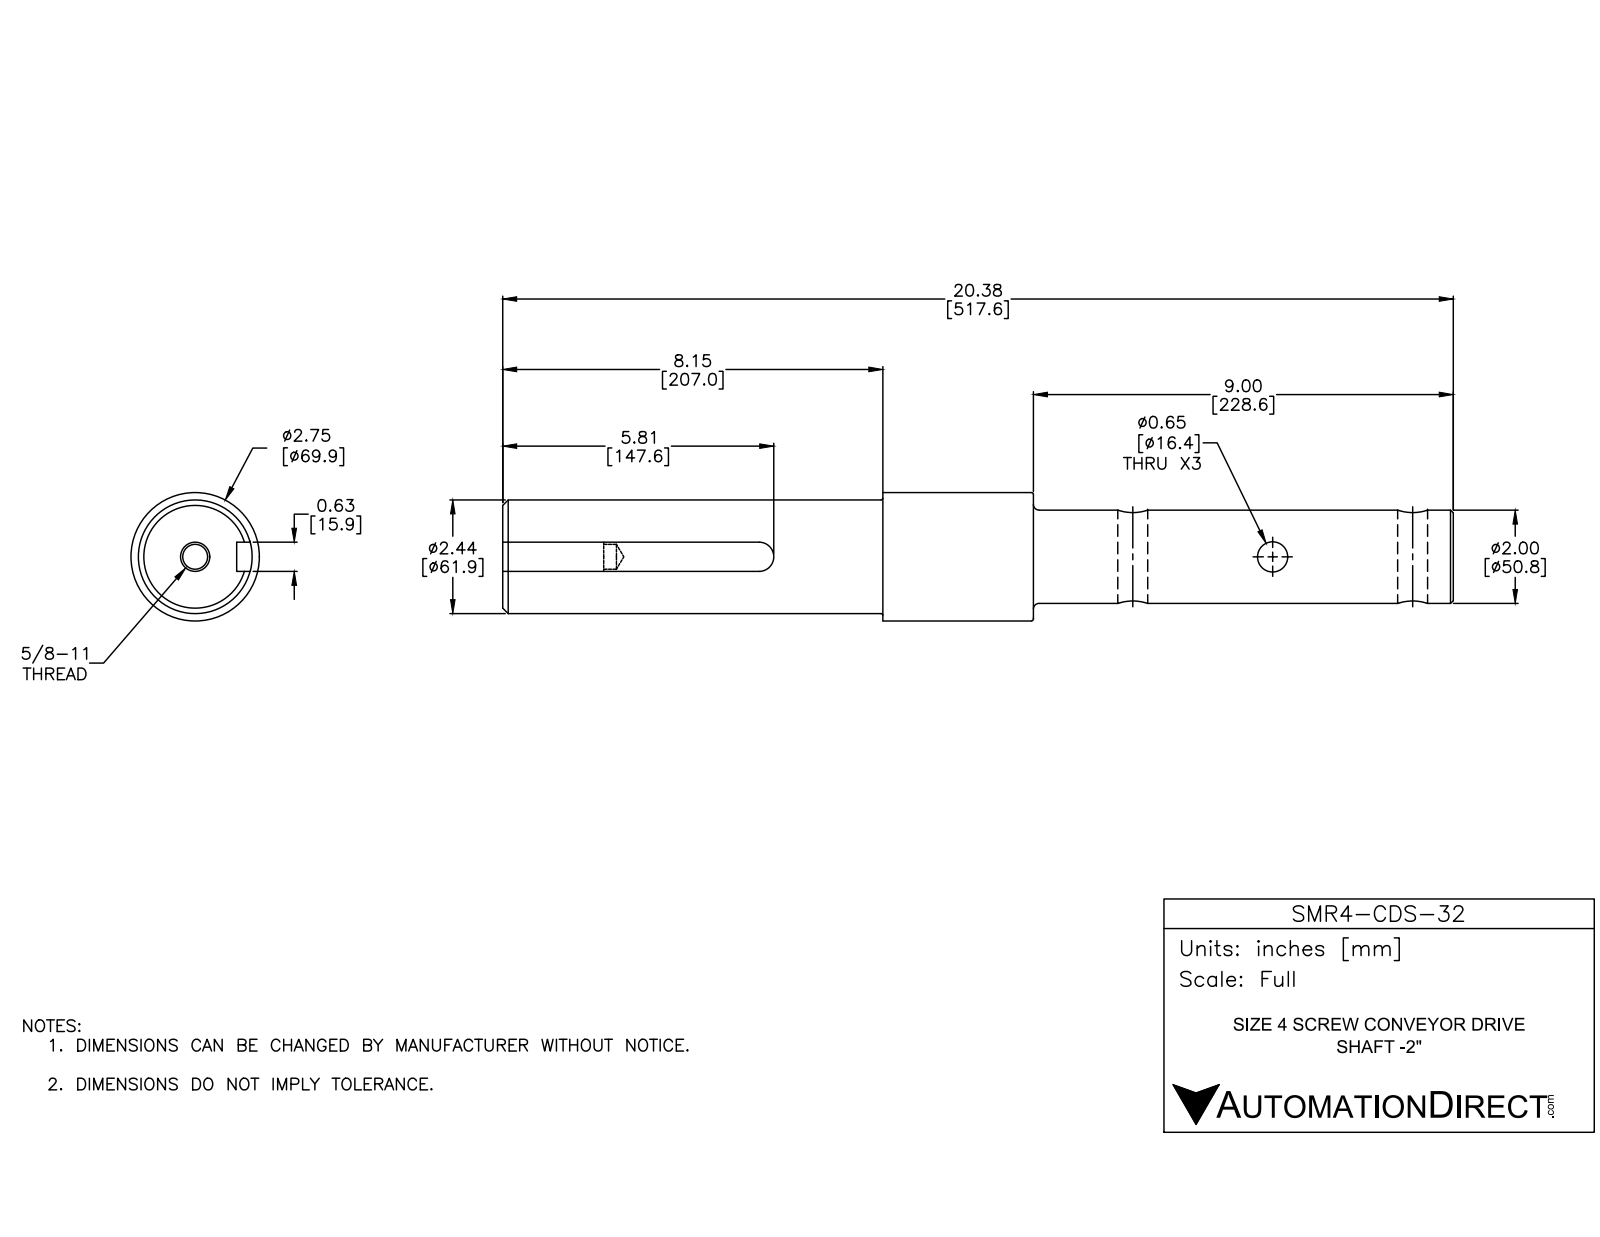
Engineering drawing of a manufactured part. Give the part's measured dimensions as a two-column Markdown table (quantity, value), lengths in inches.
| quantity | value |
| --- | --- |
| part name | SMR4-CDS-32 |
| STEP written by | SolidWorks 2016 (AUTOMOTIVE_DESIGN) |
| units | inches |
| bodies | 1 solid, 38 faces (8 planar, 18 cylindrical, 12 other) |
| overall size | 20.378 × 2.75 × 2.75 |
| volume | 81.65 in³ |
| surface area | 175.2 in² |
| round holes (diameter × count) | 0.642 × 3, 0.531 × 1, 0.625 × 1 |
| round bosses / shafts (diameter × count) | 2.75 × 1, 2.437 × 1, 2 × 1 |
| partial cylindrical surfaces (radius × count) | 0.312 × 1 |
| main face-to-face distances | 20.378, 11.378, 9, 0.625, 8.15, 3.228, 12.228, 2.165, 5.984, 9.213 |
| hole center spacings | 6 |
